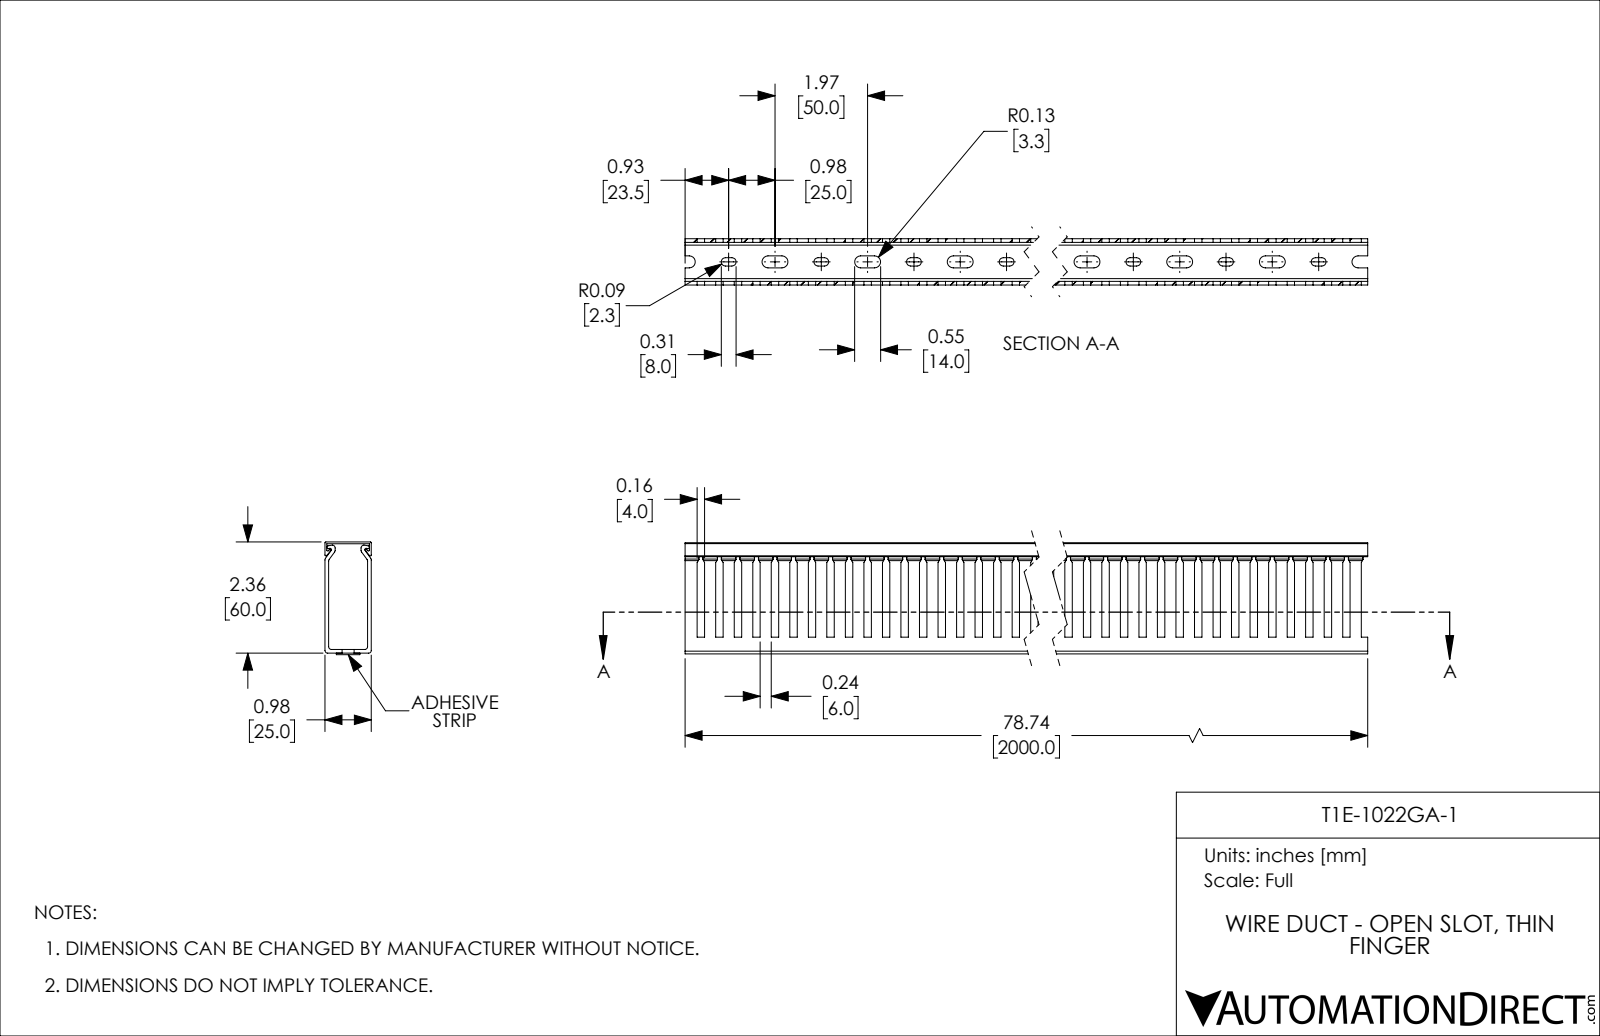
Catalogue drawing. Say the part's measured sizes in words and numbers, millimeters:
The part is named "T1E-1022GA-1". Its 3-D file was written by "SolidWorks 2021 (CONFIG_CONTROL_DESIGN)". It is 3 solids with 951 faces: 520 planar, 431 cylindrical and 0 other. Overall it measures 2000 by 60.79 by 25 millimeters. Its volume is 663 770 cubic millimeters and its surface area 789 330 square millimeters. Partial cylindrical surfaces (rounded edges, fillets, slot ends): 80 of radius 2.25, 80 of radius 3.25, 12 of radius 1.5, 8 of radius 0.5, 6 of radius 0.75. The main face-to-face distances are 2, 23, 25, 21, 1, 60, 59, 57, 58, 0.79.
